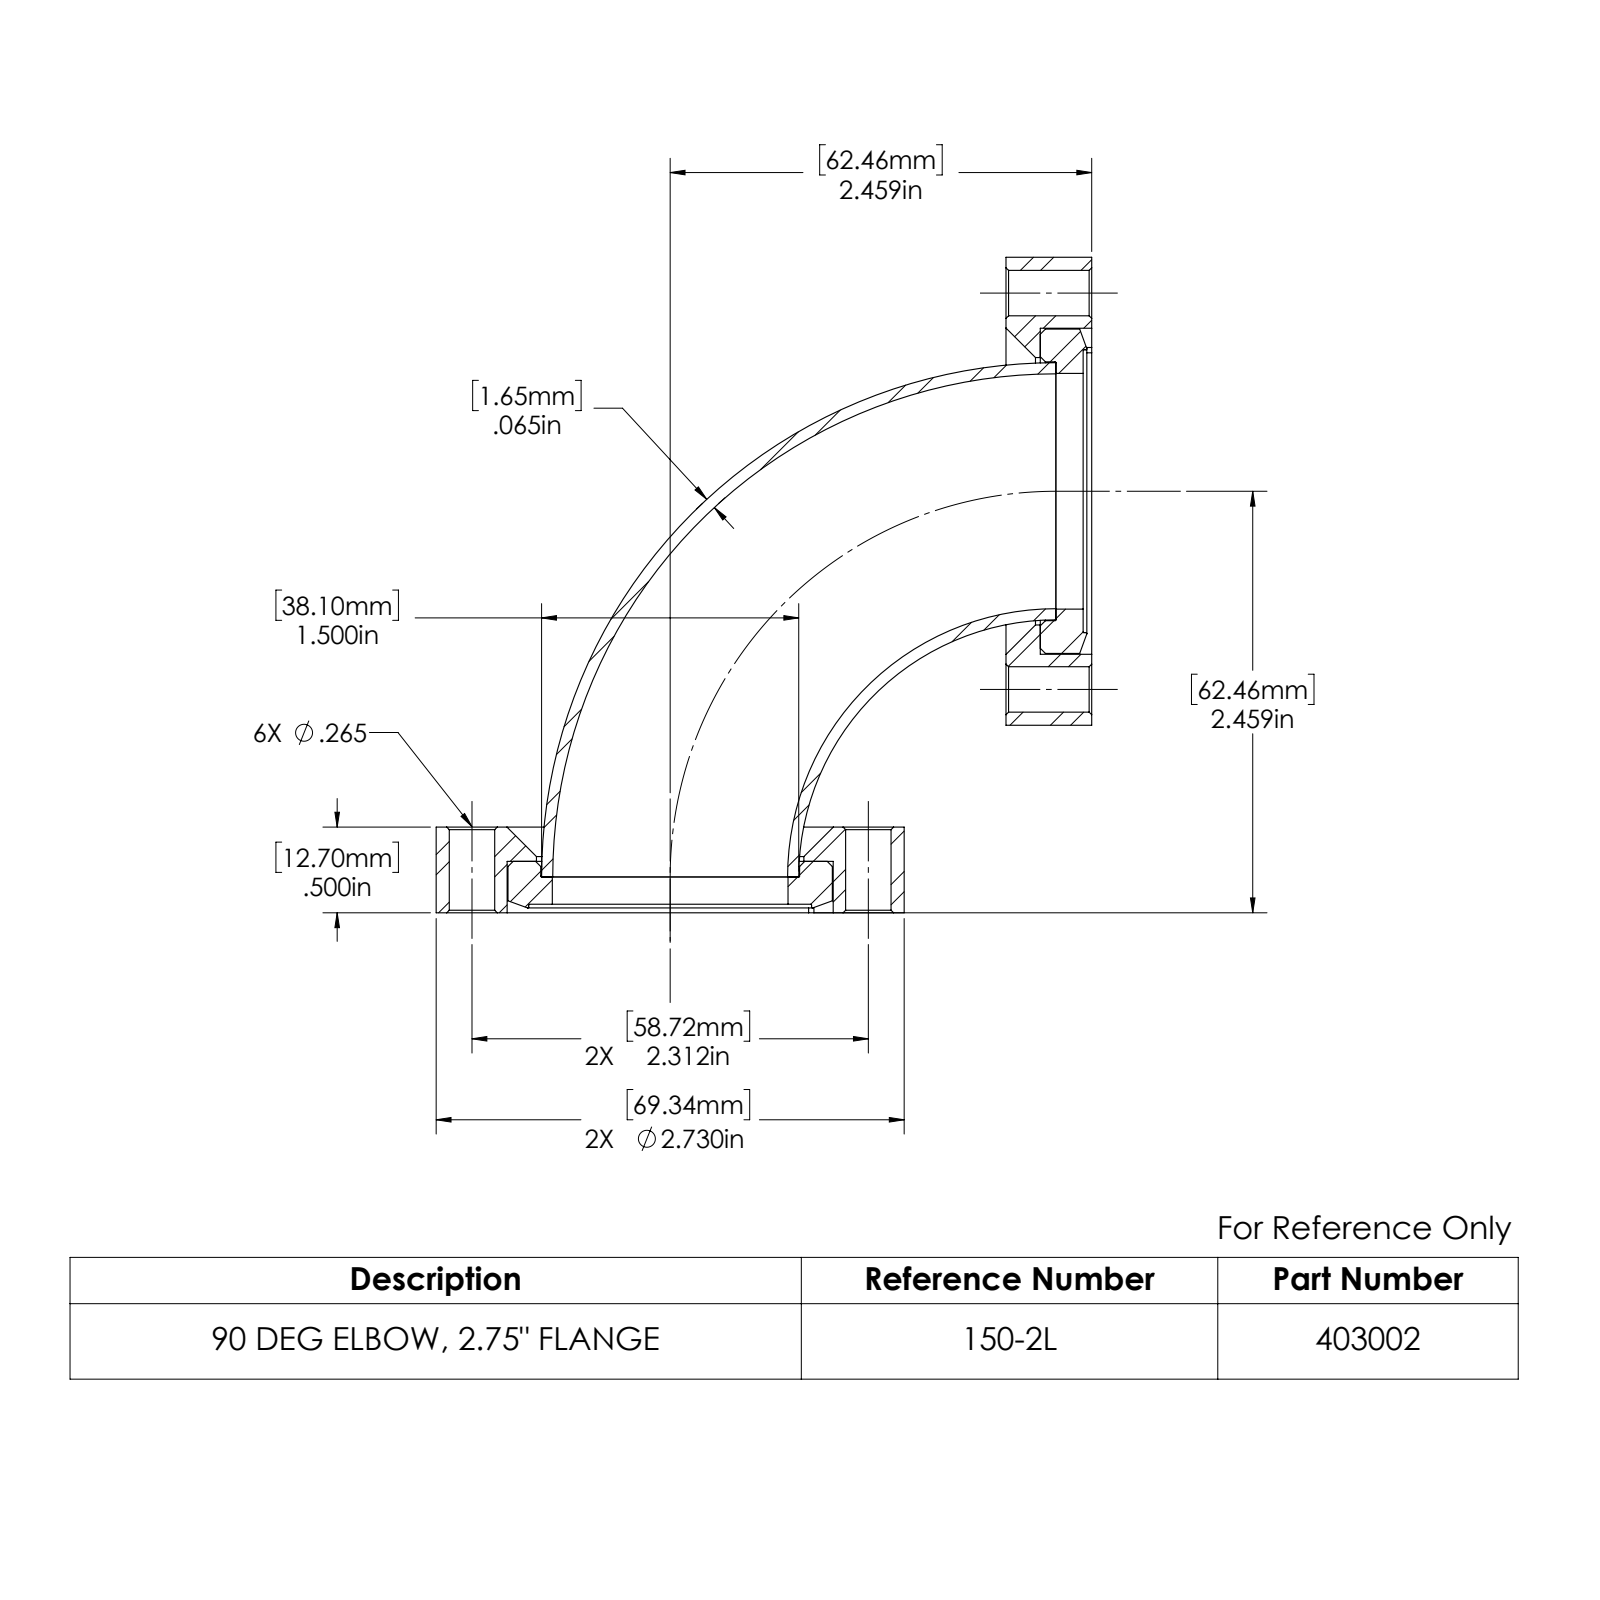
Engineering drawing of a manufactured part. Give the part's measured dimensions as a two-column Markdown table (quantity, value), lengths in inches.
| quantity | value |
| --- | --- |
| part name | 910014; 403502; 403002; 915002 |
| STEP written by | SolidWorks 2022 (AUTOMOTIVE_DESIGN) |
| units | inches |
| bodies | 5 solids, 160 faces (28 planar, 52 cylindrical, 80 other) |
| overall size | 3.824 × 3.824 × 2.73 |
| volume | 4.525 in³ |
| surface area | 75.26 in² |
| round holes (diameter × count) | 0.265 × 12, 1.375 × 2, 1.51 × 2, 1.56 × 2, 1.65 × 2, 1.902 × 2 |
| round bosses / shafts (diameter × count) | 2.73 × 2, 1.892 × 2 |
| main face-to-face distances | 0.5, 0.3, 0.2, 0.05, 0.25, 0.45, 0.209, 0.159, 0.091, 0.291 |
| hole center spacings | 1.156, 2.002, 2.002, 2.312, 2.312 |
